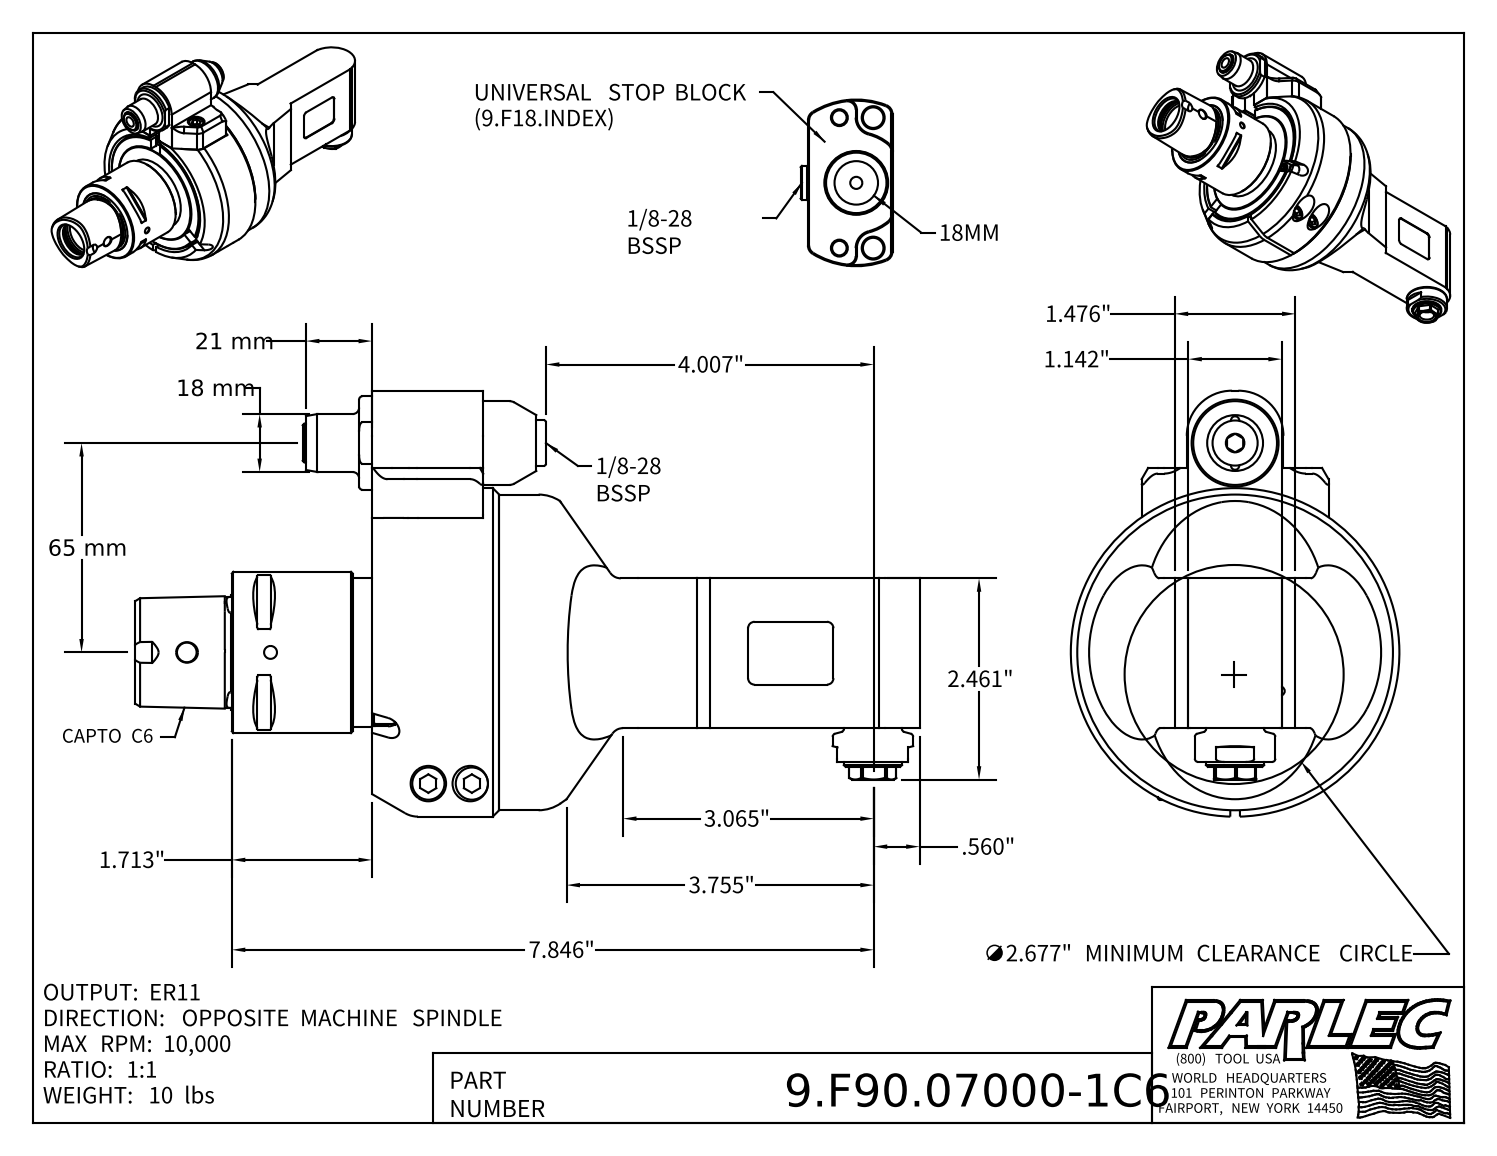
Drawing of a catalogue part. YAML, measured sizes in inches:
part_name: "9.F90.07000-1C6; 9_GA1_656_2 (Type 1, Capto C6, 65mm); 9_F90_07000"
step_written_by: "Autodesk Inventor 2022 (AUTOMOTIVE_DESIGN)"
units: inches
bodies: {solids: 5, faces: 504, planar: 240, cylindrical: 133, other: 131}
overall_size: [9.587, 5.206, 4.016]
volume: 47.88
surface_area: 204.3
round_holes:
  - {diameter: 0.335, count: 21}
  - {diameter: 0.102, count: 2}
  - {diameter: 0.165, count: 2}
  - {diameter: 0.197, count: 2}
  - {diameter: 0.409, count: 2}
  - {diameter: 0.433, count: 2}
  - {diameter: 0.098, count: 1}
  - {diameter: 0.118, count: 1}
  - {diameter: 0.157, count: 1}
  - {diameter: 0.24, count: 1}
  - {diameter: 0.256, count: 1}
  - {diameter: 0.276, count: 1}
round_bosses_or_shafts:
  - {diameter: 0.394, count: 4}
  - {diameter: 0.236, count: 4}
  - {diameter: 0.709, count: 2}
  - {diameter: 0.315, count: 2}
  - {diameter: 0.098, count: 2}
  - {diameter: 4.016, count: 1}
  - {diameter: 3.858, count: 1}
  - {diameter: 3.031, count: 1}
partial_cylinders:
  - {radius: 0.079, count: 12}
  - {radius: 0.012, count: 8}
  - {radius: 0.157, count: 5}
  - {radius: 0.02, count: 2}
  - {radius: 0.039, count: 2}
  - {radius: 0.138, count: 2}
  - {radius: 0.197, count: 2}
  - {radius: 0.551, count: 2}
face_to_face_distances: [1.26, 0.02, 1.555, 0.738, 0.276, 0.295, 1.831, 2.569, 0.335, 1.142]
hole_center_spacings: [1.516, 2.144, 1.824, 3.002, 0.835, 2.651, 2.914, 3.031]
